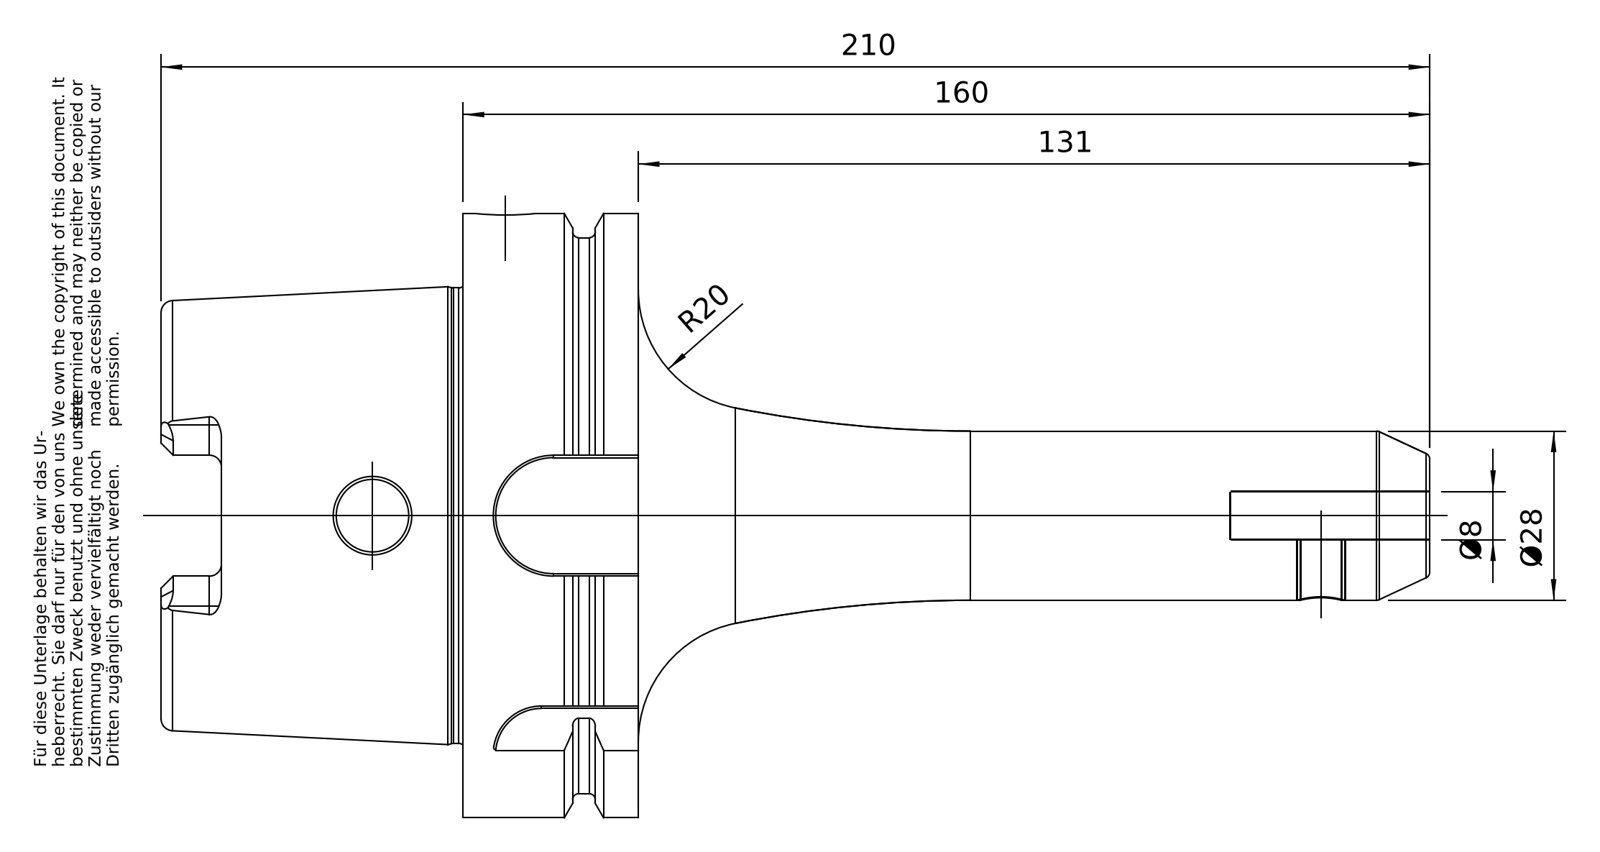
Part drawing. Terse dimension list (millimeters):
name: A100-002-08
written by: PRO/ENGINEER BY PARAMETRIC TECHNOLOGY CORPORATION, 2010430 (CONFIG_CONTROL_DESIGN)
unit: mm
bodies: 1 solid, 182 faces (50 planar, 55 cylindrical, 77 other)
size: 210 × 100 × 100
volume: 353 386 mm³; area: 62 243 mm²
holes: 2× ⌀8, 1× ⌀6.8, 1× ⌀10, 1× ⌀12, 1× ⌀22.5, 1× ⌀24, 1× ⌀24.32, 1× ⌀24.5, 1× ⌀53, 1× ⌀63
bosses: 1× ⌀100, 1× ⌀92, 1× ⌀75.36, 1× ⌀28
rounds: 6× R2, 4× R5, 1× R8, 1× R10, 1× R11
face distances: 29, 12.5, 16.5, 50, 62.5, 79, 88, 78.5, 28.5, 16
hole spacings: 135
